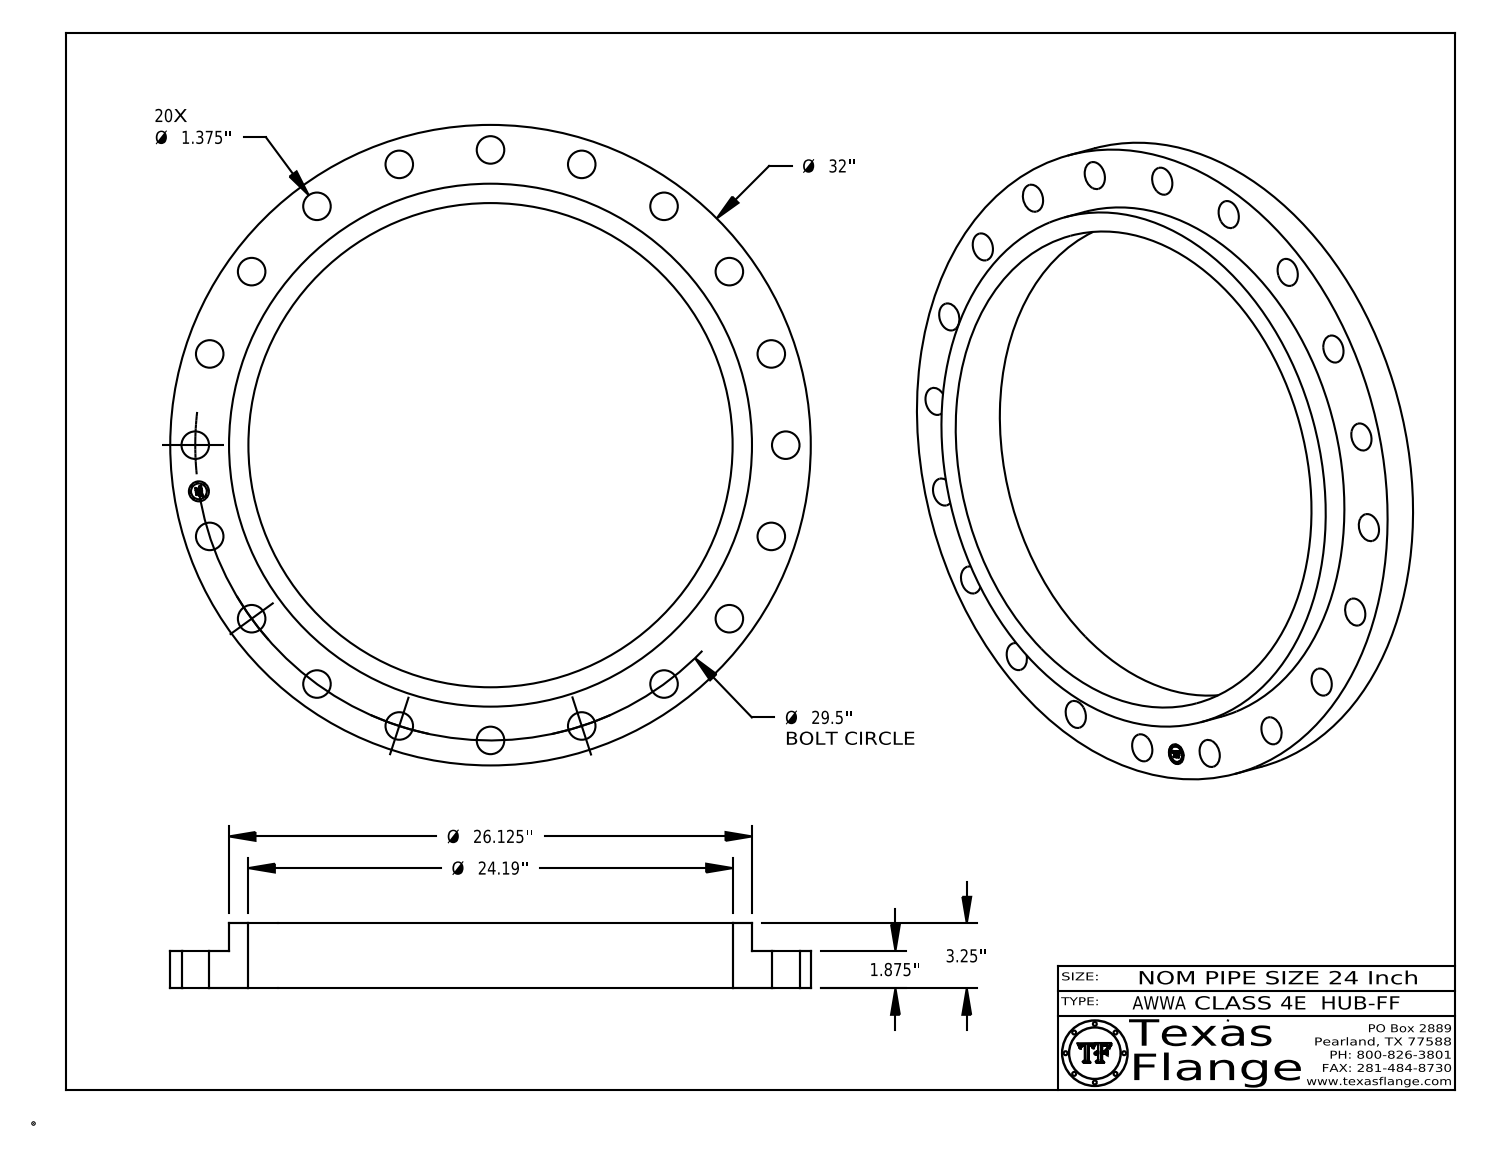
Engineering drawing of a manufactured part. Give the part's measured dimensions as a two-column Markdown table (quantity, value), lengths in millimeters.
| quantity | value |
| --- | --- |
| part name | AWWA Class 4E-HUB-FF |
| STEP written by | CATIA V5 STEP AP214 (AUTOMOTIVE_DESIGN) |
| units | millimeters |
| bodies | 1 solid, 434 faces (368 planar, 66 cylindrical, 0 other) |
| overall size | 812.8 × 812.8 × 82.6 |
| volume | 11 400 000 mm³ |
| surface area | 864 500 mm² |
| round holes (diameter × count) | 34.9 × 20, 25.4 × 1, 614.4 × 1 |
| round bosses / shafts (diameter × count) | 1.5 × 8, 812.8 × 1, 663.6 × 1, 20 × 1 |
| main face-to-face distances | 47.6, 82.6, 34.9, 0.4, 47.2, 35.3, 7.6, 7.4, 1.4, 4.9 |
| hole center spacings | 374.7, 740.1, 117.2, 440.4, 529.8, 606.2, 667.6, 231.5 |
